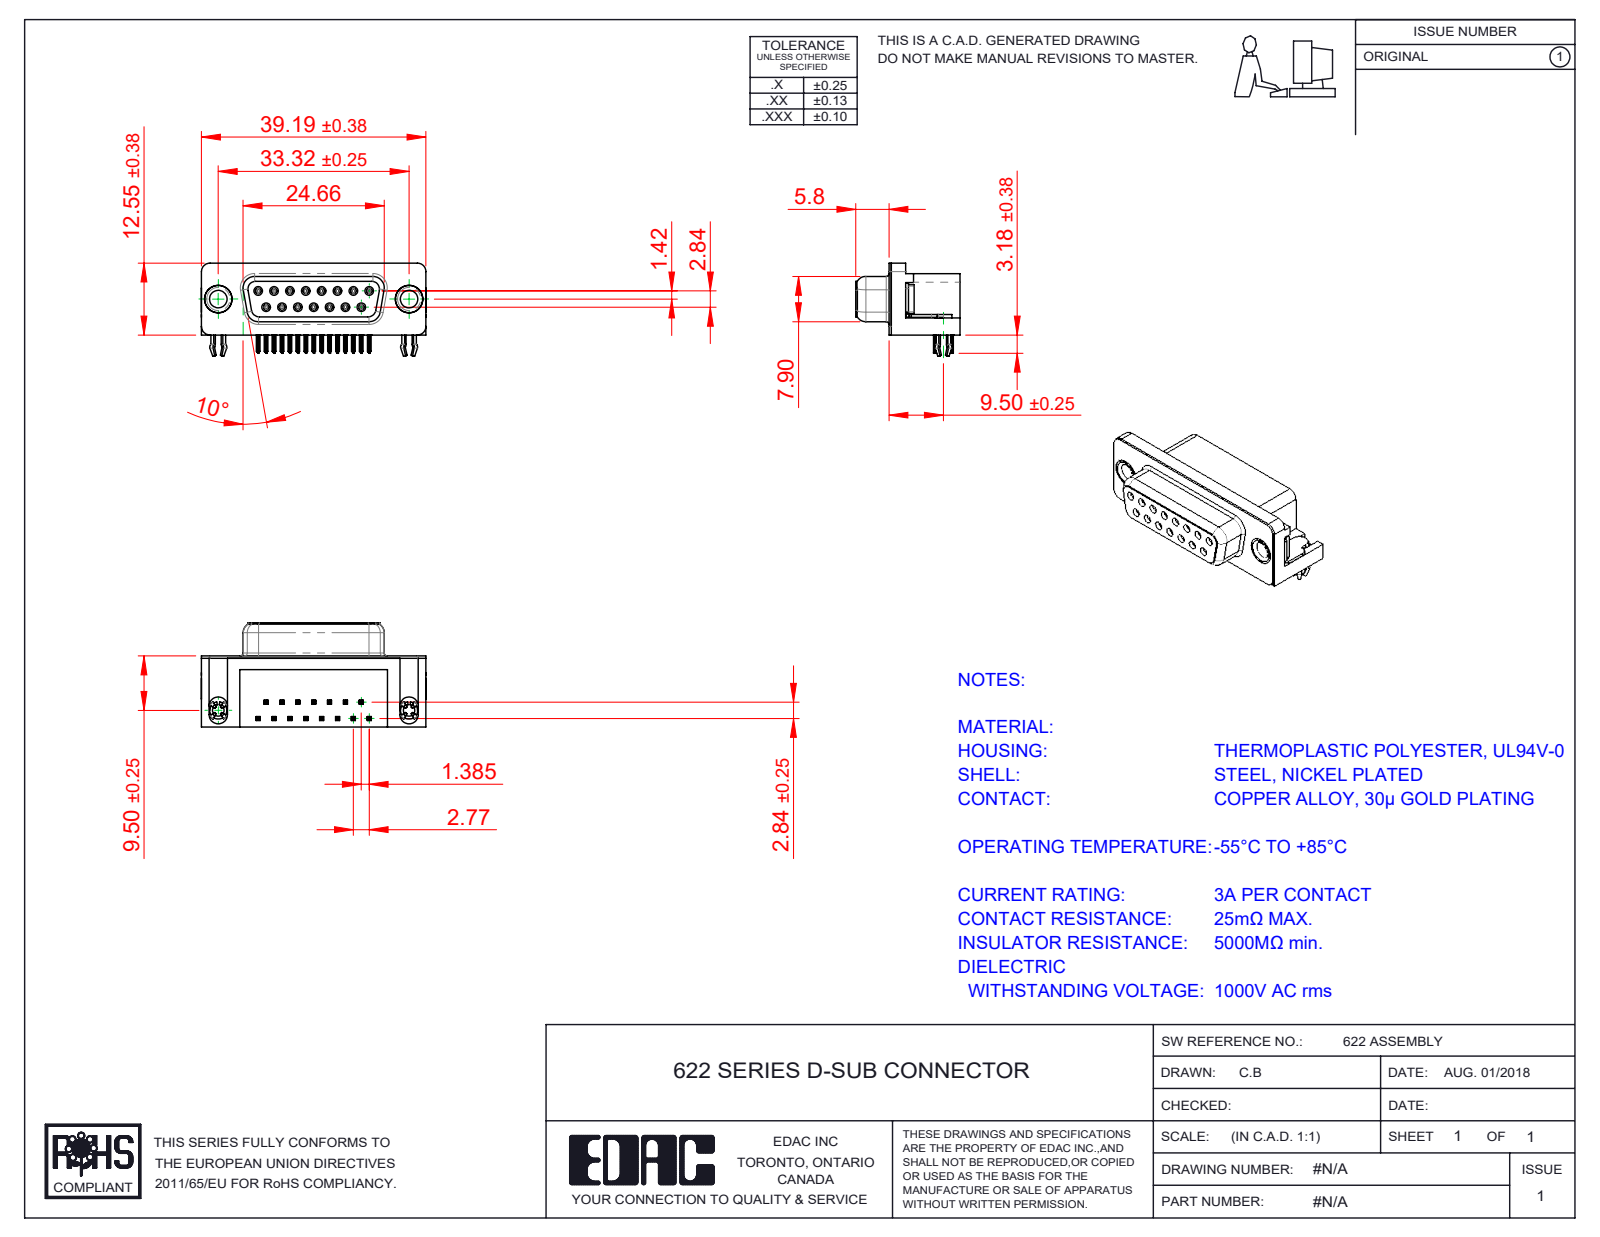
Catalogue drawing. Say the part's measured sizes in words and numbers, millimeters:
The part is named "622 Housing_15 Socket; 622-015-660-051; 622 Socket Bottom; 622 4-40 Threaded Board Mount (+3 more)". Its 3-D file was written by "SolidWorks 2016 (CONFIG_CONTROL_DESIGN)". It is 21 solids with 2417 faces: 1074 planar, 599 cylindrical and 744 other. Overall it measures 39.22 by 18.2 by 15.73 millimeters. Its volume is 5 187 cubic millimeters and its surface area 6 771 square millimeters. Round holes: 15 of diameter 0.8, 15 of diameter 0.9, 2 of diameter 2.26, 2 of diameter 3.05, 2 of diameter 4, 2 of diameter 4.8, 2 of diameter 5. Round bosses or shafts: 15 of diameter 1.2, 2 of diameter 4.9, 2 of diameter 4.75, 2 of diameter 3.85, 2 of diameter 3.26. Partial cylindrical surfaces (rounded edges, fillets, slot ends): 120 of radius 0.1, 60 of radius 0.15, 30 of radius 0.35, 18 of radius 1, 15 of radius 0.34, 8 of radius 0.25, 8 of radius 1.35, 8 of radius 1.5. The main face-to-face distances are 0.4, 12, 6.2, 12.4, 10.35, 2.9, 6.65, 0.85, 0.35, 5.8. The hole center spacings are 3.16, 2.77, 5.54, 8.31, 11.08, 5.03, 5.04, 7.48.
